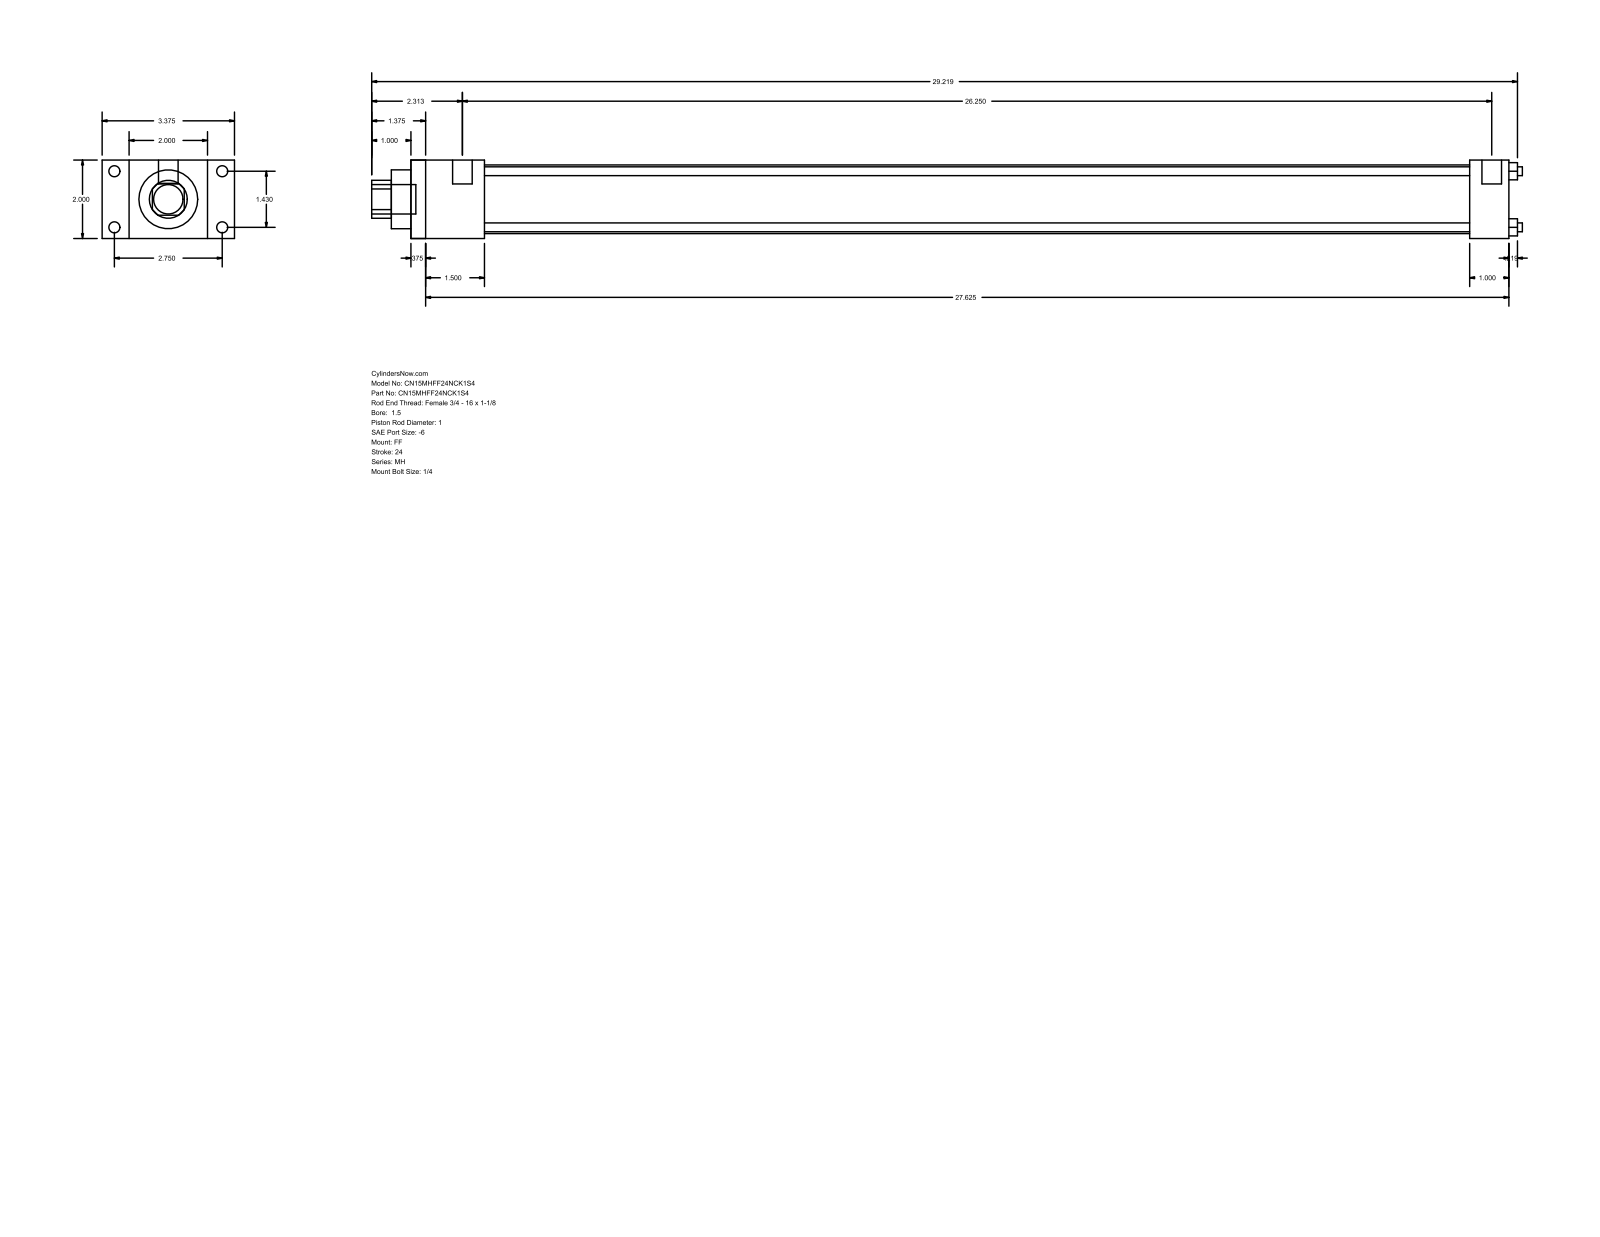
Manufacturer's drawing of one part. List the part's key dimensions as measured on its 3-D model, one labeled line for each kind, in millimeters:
Part name (STEP PRODUCT): MH_FF__0150_1
STEP written by: GSSL Pune (CONFIG_CONTROL_DESIGN)
Units: millimetres
Bodies: 0 solids, 92 faces (64 planar, 28 cylindrical, 0 other)
Overall size (bounding box): 745.33 × 85.72 × 50.8
Round holes (diameter × count): ⌀5.71 ×4, ⌀25.4 ×1, ⌀38.1 ×1, ⌀44.45 ×1
Round bosses / shafts (diameter × count): ⌀7.14 ×4, ⌀5.56 ×4, ⌀12.7 ×2, ⌀19.05 ×1
Partial cylindrical surfaces — rounded edges, fillets, slot ends (radius × count): R12.29 ×1
Main face-to-face distances: 50.8, 711.2, 9.52, 701.68, 25.4, 17.46, 68.26, 47.63, 38.11, 663.57
Hole centre spacings: 25.68, 36.32, 51.36
